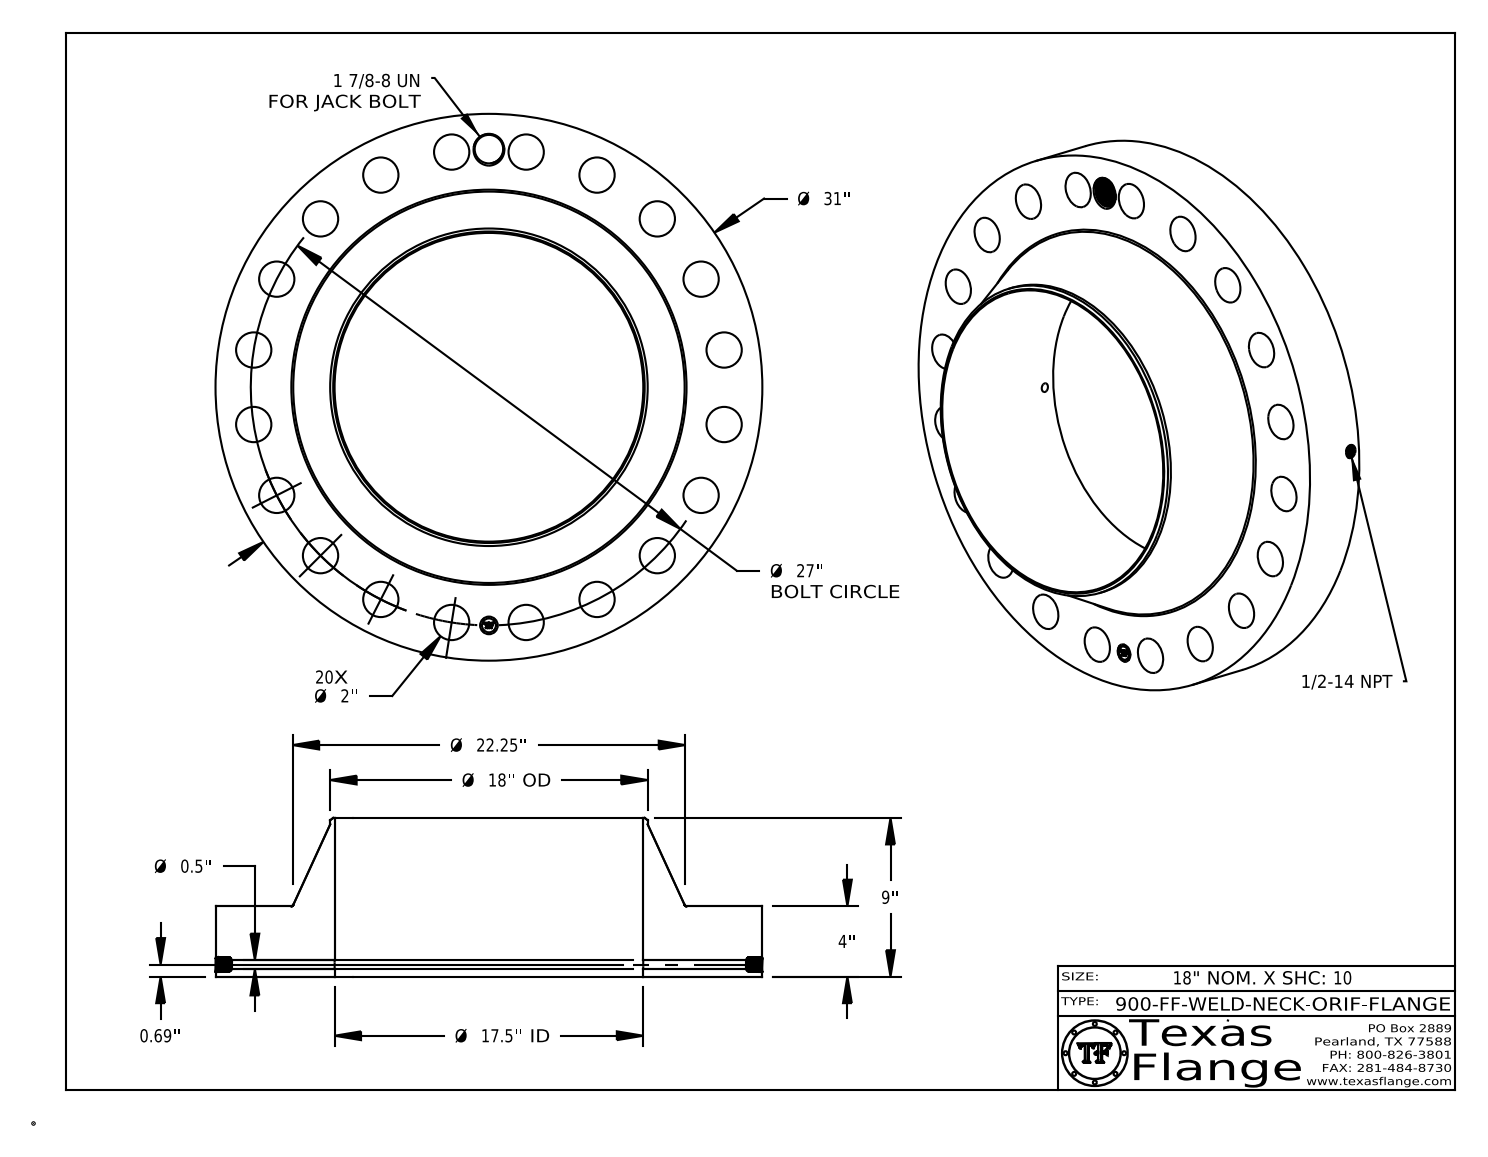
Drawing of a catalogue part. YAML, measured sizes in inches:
part_name: "900-FF-WELD-NECK"
step_written_by: "CATIA V5 STEP AP214 (AUTOMOTIVE_DESIGN)"
units: inches
bodies: {solids: 1, faces: 892, planar: 368, cylindrical: 149, other: 375}
overall_size: [31, 31, 9]
volume: 2162
surface_area: 2563
round_holes:
  - {diameter: 2, count: 20}
  - {diameter: 0.5, count: 1}
  - {diameter: 0.672, count: 1}
  - {diameter: 1, count: 1}
  - {diameter: 1.615, count: 1}
  - {diameter: 17.5, count: 1}
round_bosses_or_shafts:
  - {diameter: 0.061, count: 8}
  - {diameter: 31, count: 1}
  - {diameter: 18, count: 1}
  - {diameter: 0.788, count: 1}
face_to_face_distances: [4, 9, 5, 3.985, 0.015, 5.015, 0.298, 0.293, 0.054, 0.248]
hole_center_spacings: [13.5, 19.092, 25.679, 26.668, 12.258, 4.224, 8.344, 15.87]
